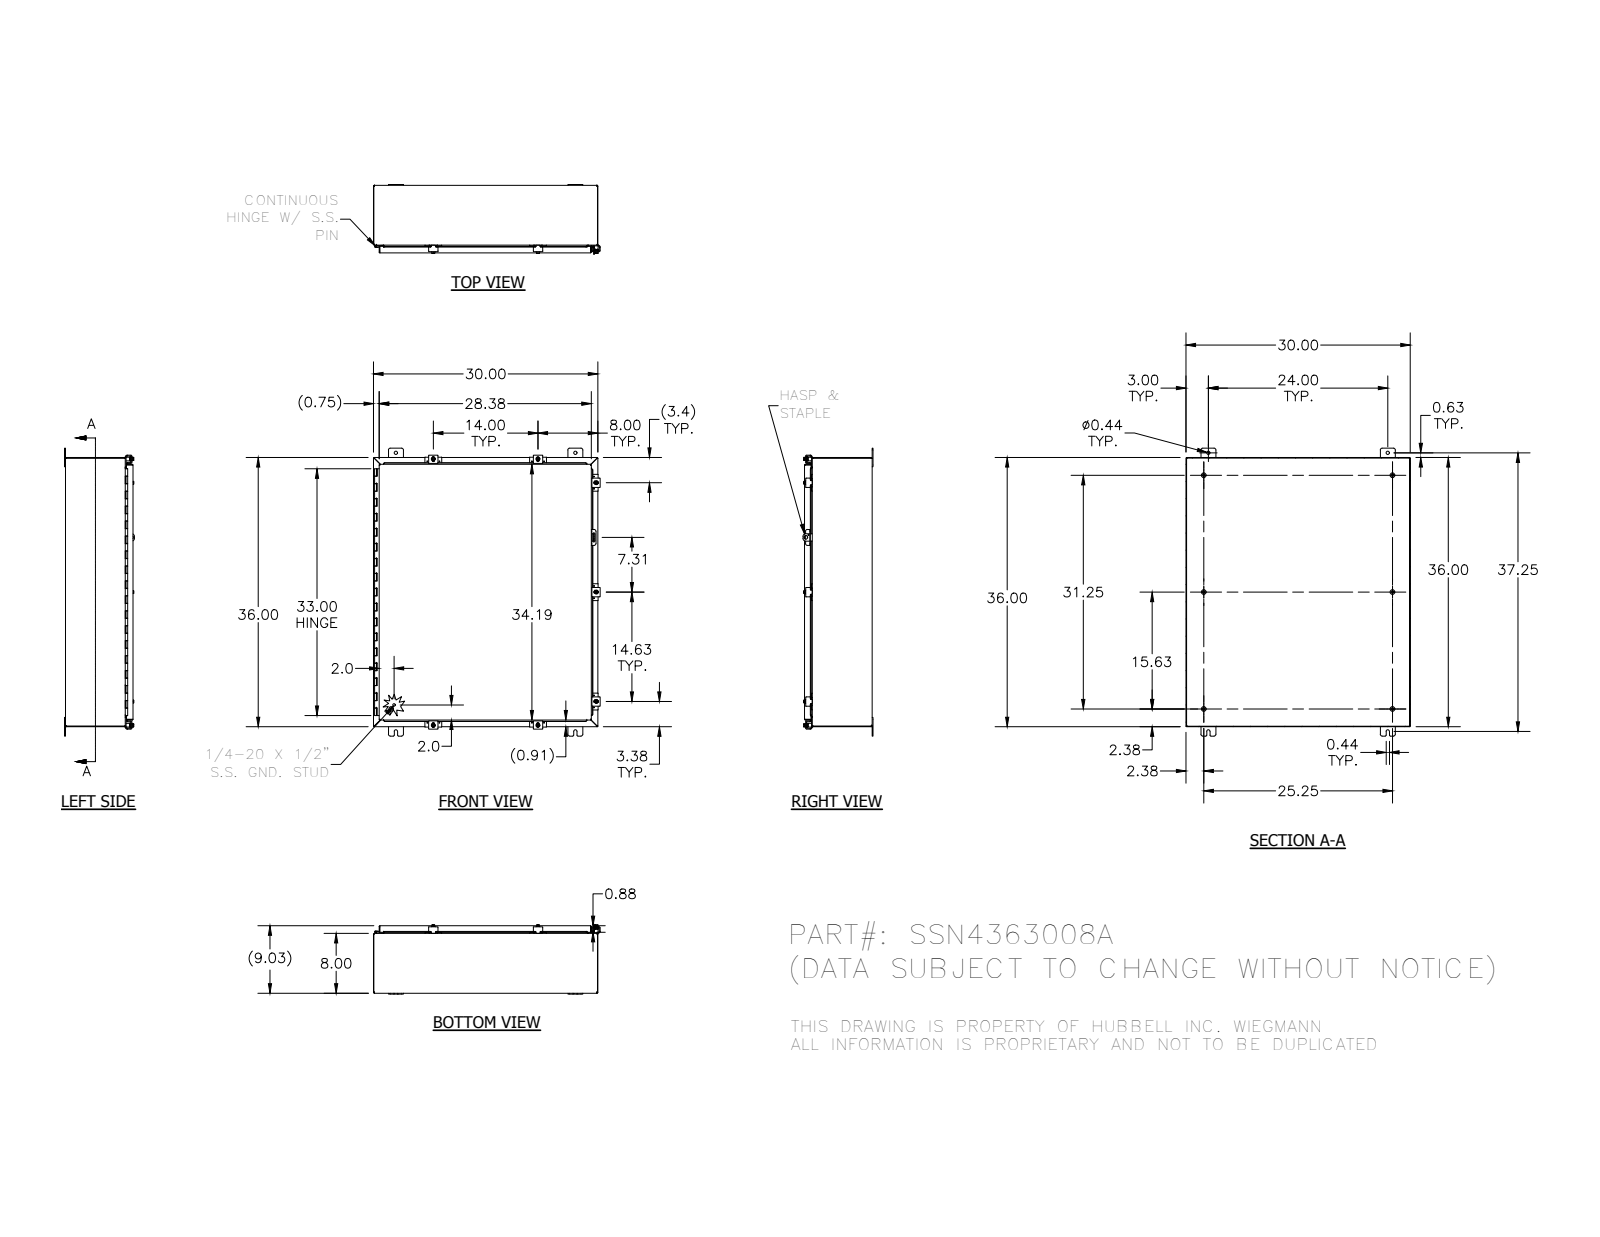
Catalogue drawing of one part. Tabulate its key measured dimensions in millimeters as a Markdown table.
| quantity | value |
| --- | --- |
| part name | SSN4363008A; 32874-36L; 30824-4; 30824-3 (+8 more) |
| STEP written by | SolidWorks 2014 (AUTOMOTIVE_DESIGN) |
| units | millimeters |
| bodies | 54 solids, 2180 faces (862 planar, 947 cylindrical, 371 other) |
| overall size | 977.9 × 767.5 × 237.6 |
| volume | 4 636 000 mm³ |
| surface area | 4 812 000 mm² |
| round holes (diameter × count) | 2.8 × 14, 5.4 × 7, 7.1 × 7, 7.6 × 7, 11.1 × 4, 3.2 × 1, 4 × 1, 12.7 × 1 |
| round bosses / shafts (diameter × count) | 6.4 × 9, 13.2 × 7, 12.7 × 7, 8.9 × 7, 15.9 × 6, 8.4 × 6, 8.6 × 1, 3 × 1 |
| partial cylindrical surfaces (radius × count) | 0.8 × 83, 3.2 × 37, 6.4 × 33, 0.8 × 23, 2.7 × 23, 1.6 × 18, 3.6 × 14, 2.5 × 10 |
| main face-to-face distances | 1.9, 227.6, 225.7, 229.4, 760.1, 912.5, 201.3, 26.2, 762, 758.2 |
| hole center spacings | 22.3, 896.6, 355.6, 41.3, 335.1, 371.5, 376.3, 392.2 |
